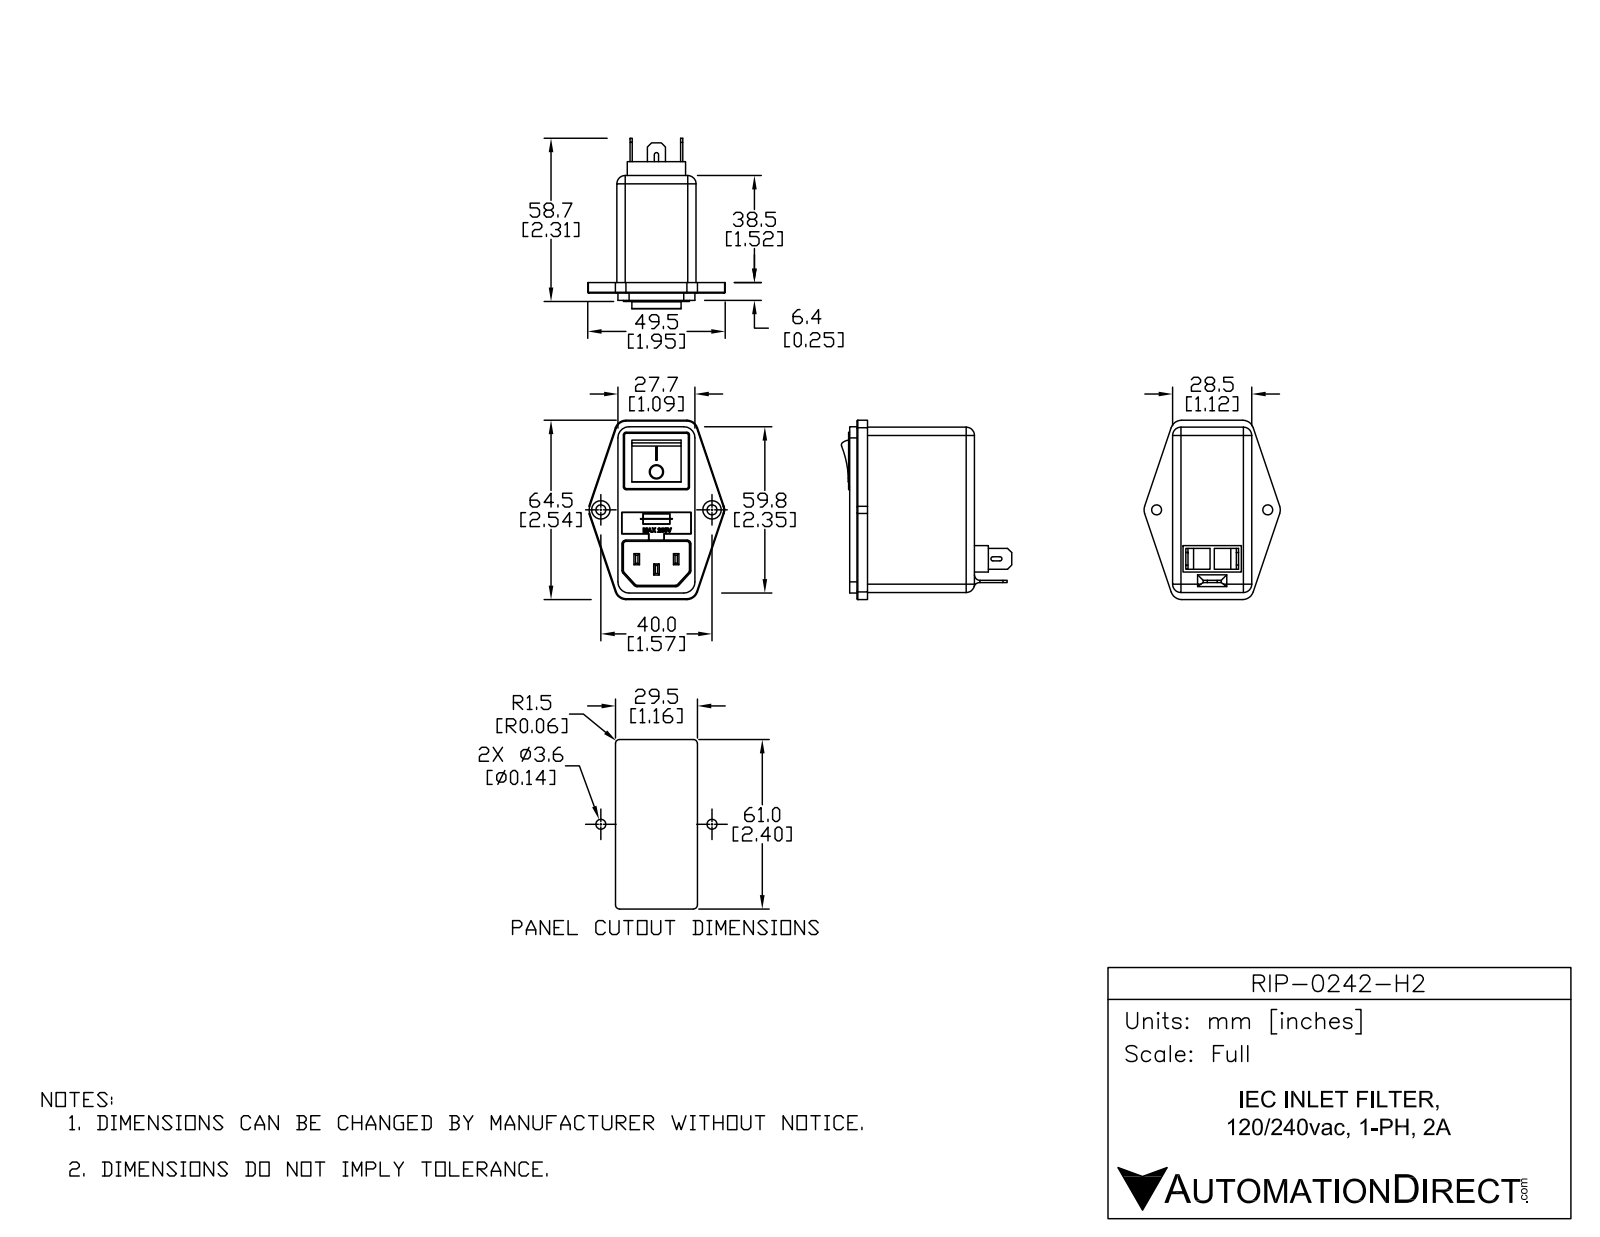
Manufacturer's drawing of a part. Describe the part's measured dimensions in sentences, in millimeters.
The part is named "RIP0242H2". Its 3-D file was written by "SolidWorks 2015 (AUTOMOTIVE_DESIGN)". It is 1 solid with 386 faces: 244 planar, 87 cylindrical and 55 other. Overall it measures 64.5 by 61.32 by 49.16 millimeters. Its volume is 73 796 cubic millimeters and its surface area 15 879 square millimeters. Round holes: 2 of diameter 3.6. Partial cylindrical surfaces (rounded edges, fillets, slot ends): 11 of radius 1, 10 of radius 4, 8 of radius 3, 7 of radius 0.4, 6 of radius 0.1, 5 of radius 2, 4 of radius 0.15, 4 of radius 0.6. The main face-to-face distances are 28.5, 2.6, 59.5, 3.8, 6.4, 38.5, 44.9, 42.3, 2.5, 0.4. The hole center spacings are 40.
